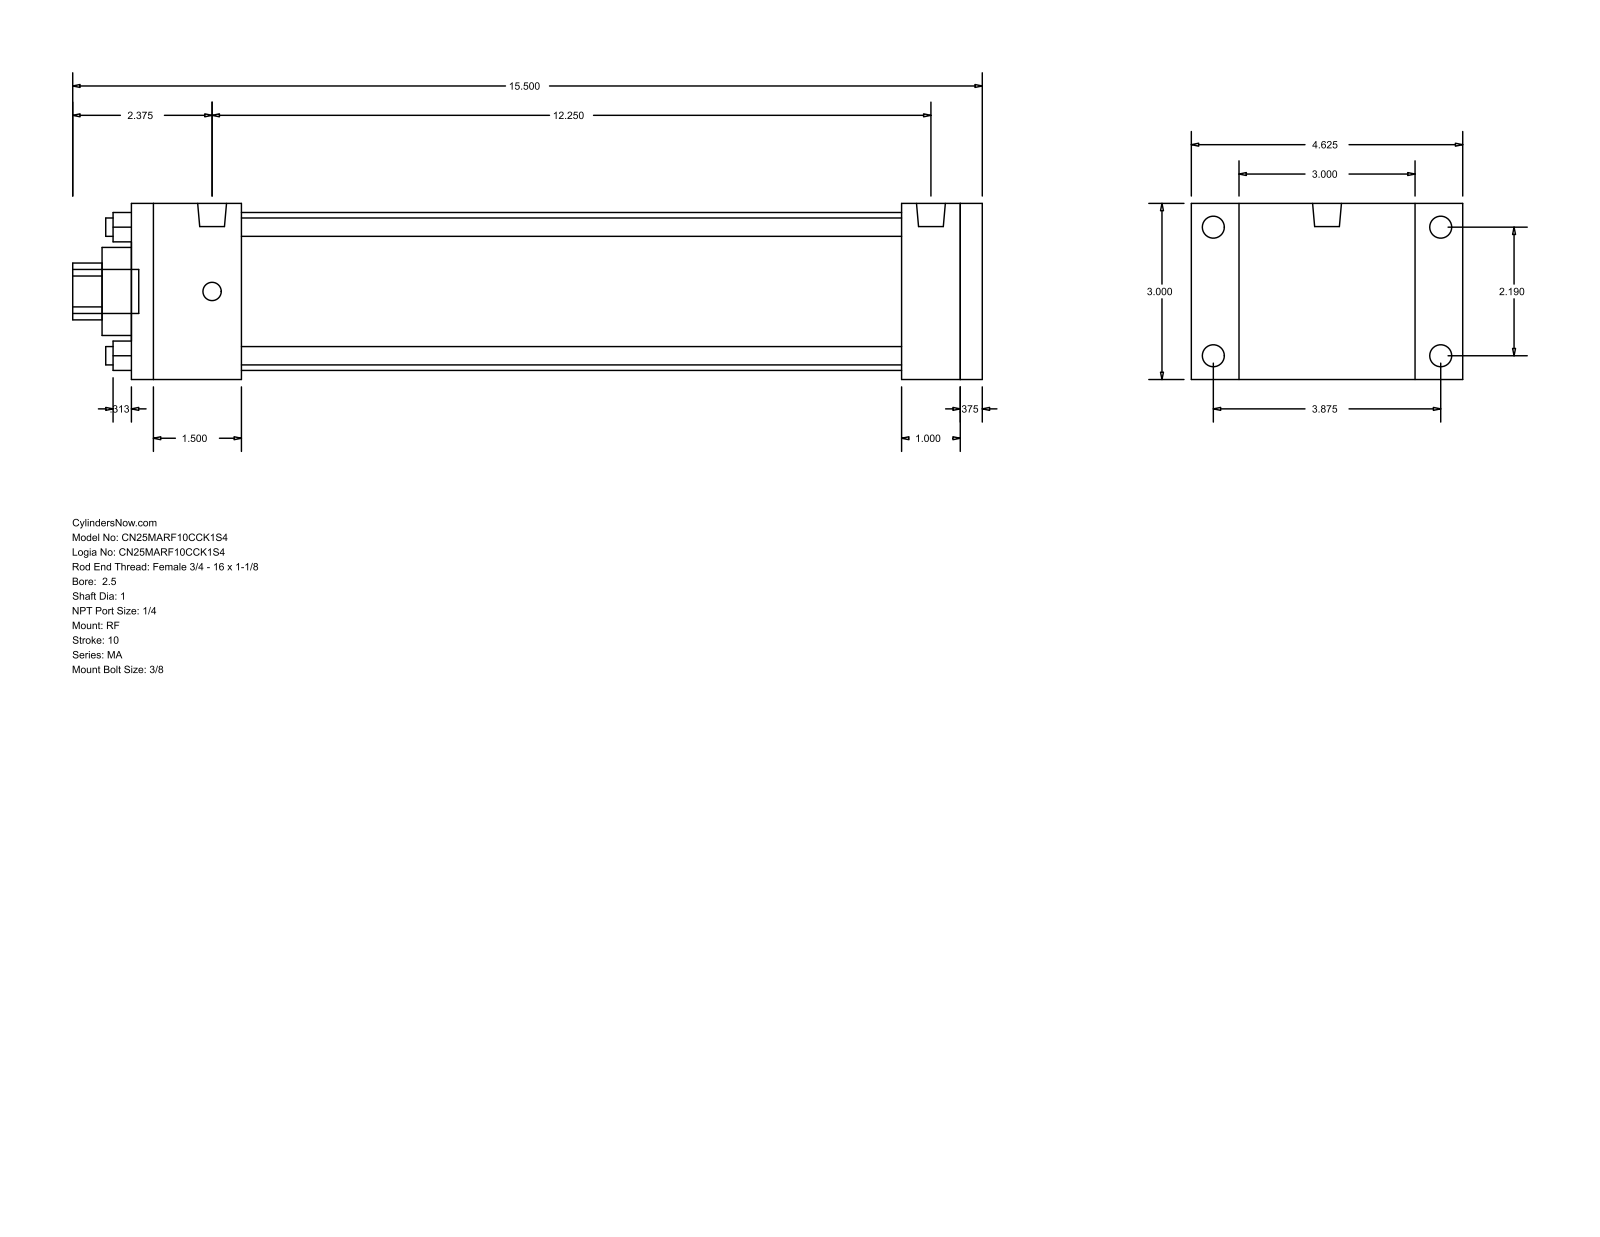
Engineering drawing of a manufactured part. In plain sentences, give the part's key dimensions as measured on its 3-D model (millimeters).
The part is named "MA_RF__0250_1". Its 3-D file was written by "GSSL Pune (CONFIG_CONTROL_DESIGN)". It is 0 solids with 92 faces: 64 planar, 28 cylindrical and 0 other. Overall it measures 393.7 by 117.47 by 76.2 millimeters. Round holes: 4 of diameter 7.94, 1 of diameter 25.4, 1 of diameter 38.1, 1 of diameter 68.33. Round bosses or shafts: 4 of diameter 9.53, 4 of diameter 7.94, 2 of diameter 12.49, 1 of diameter 19.05. Partial cylindrical surfaces (rounded edges, fillets, slot ends): 1 of radius 12.29. The main face-to-face distances are 76.2, 368.3, 358.78, 9.52, 47.63, 333.37, 285.74, 311.15, 320.67, 25.41. The hole center spacings are 39.33, 55.62, 78.66.
